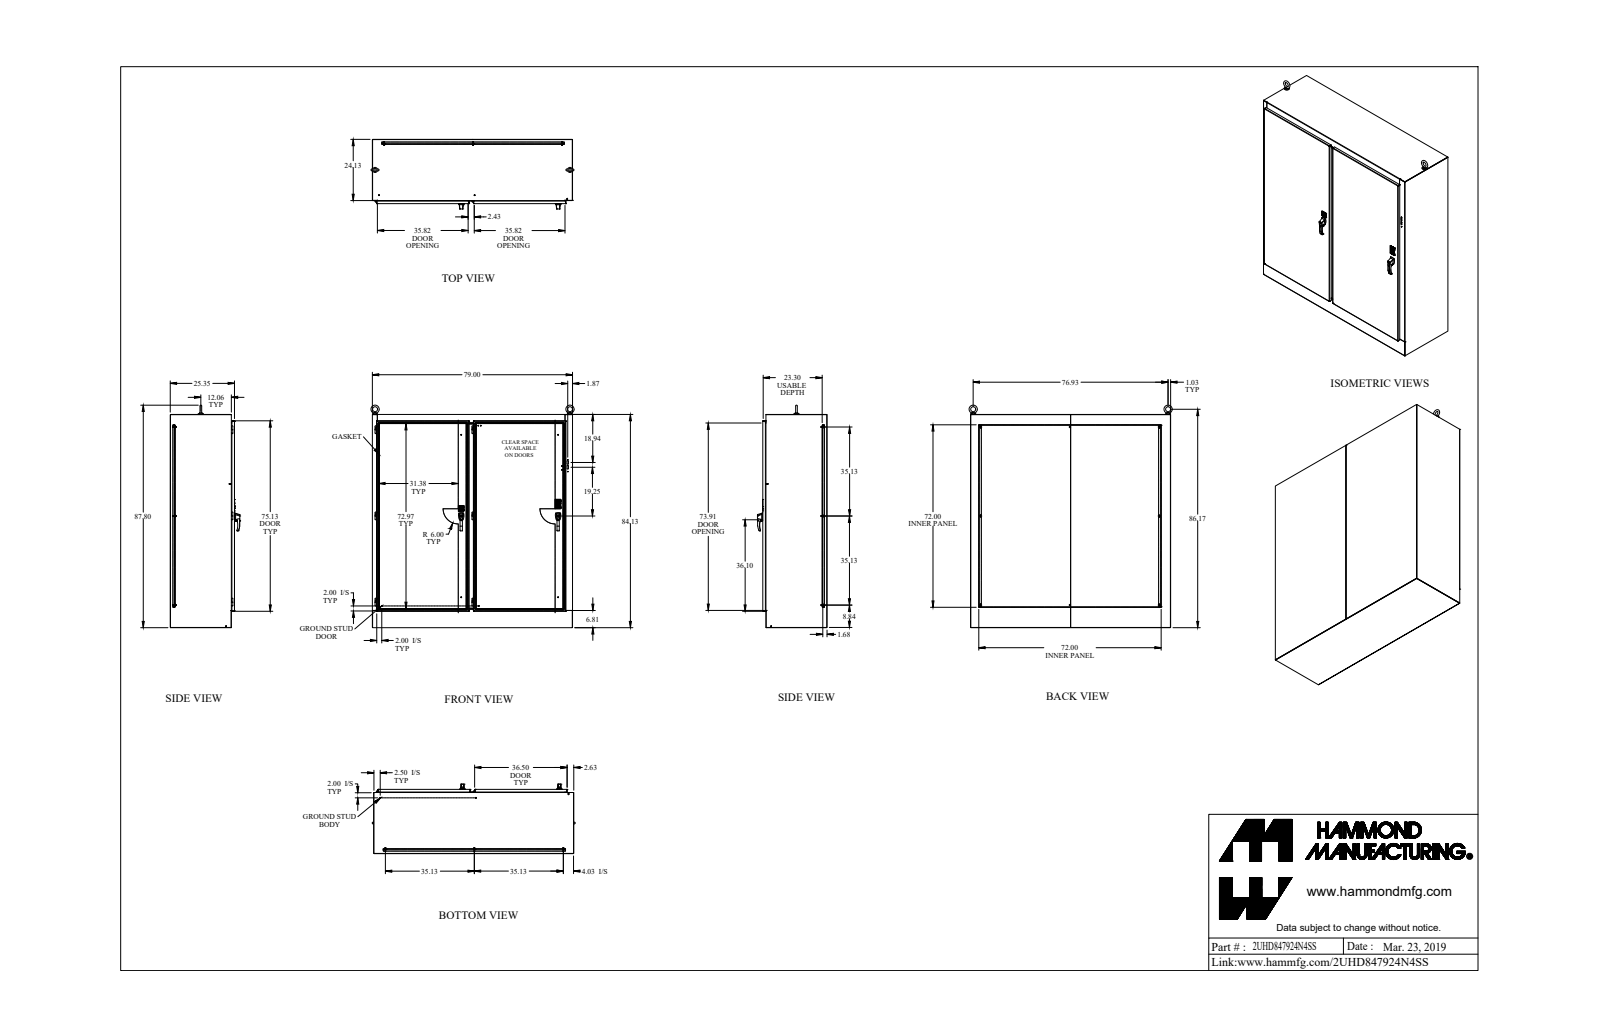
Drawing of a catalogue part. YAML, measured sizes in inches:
part_name: "2UHD847924N4SS"
step_written_by: "SolidWorks 2018 (AUTOMOTIVE_DESIGN)"
units: inches
bodies: {solids: 223, faces: 3338, planar: 1961, cylindrical: 990, other: 387}
overall_size: [87.799, 80.182, 27.466]
volume: 5033
surface_area: 62267
round_holes:
  - {diameter: 0.25, count: 15}
  - {diameter: 0.196, count: 13}
  - {diameter: 0.281, count: 9}
  - {diameter: 0.307, count: 9}
  - {diameter: 0.35, count: 8}
  - {diameter: 0.201, count: 6}
  - {diameter: 0.257, count: 6}
  - {diameter: 0.313, count: 6}
  - {diameter: 0.313, count: 6}
  - {diameter: 0.255, count: 5}
  - {diameter: 0.445, count: 5}
  - {diameter: 0.156, count: 4}
round_bosses_or_shafts:
  - {diameter: 0.25, count: 18}
  - {diameter: 1, count: 12}
  - {diameter: 0.65, count: 9}
  - {diameter: 0.375, count: 9}
  - {diameter: 0.332, count: 8}
  - {diameter: 0.75, count: 6}
  - {diameter: 0.5, count: 6}
  - {diameter: 0.293, count: 6}
partial_cylinders:
  - {radius: 0.125, count: 67}
  - {radius: 0.5, count: 42}
  - {radius: 0.06, count: 35}
  - {radius: 0.017, count: 32}
  - {radius: 0.048, count: 30}
  - {radius: 0.143, count: 30}
  - {radius: 0.03, count: 28}
  - {radius: 0.25, count: 26}
face_to_face_distances: [0.095, 0.046, 23.461, 25.368, 25.273, 1.907, 1.812, 1.86, 1.765, 23.508]
hole_center_spacings: [1.72, 70.25, 1, 3.43, 35.125, 35.125, 78.542, 78.542]
